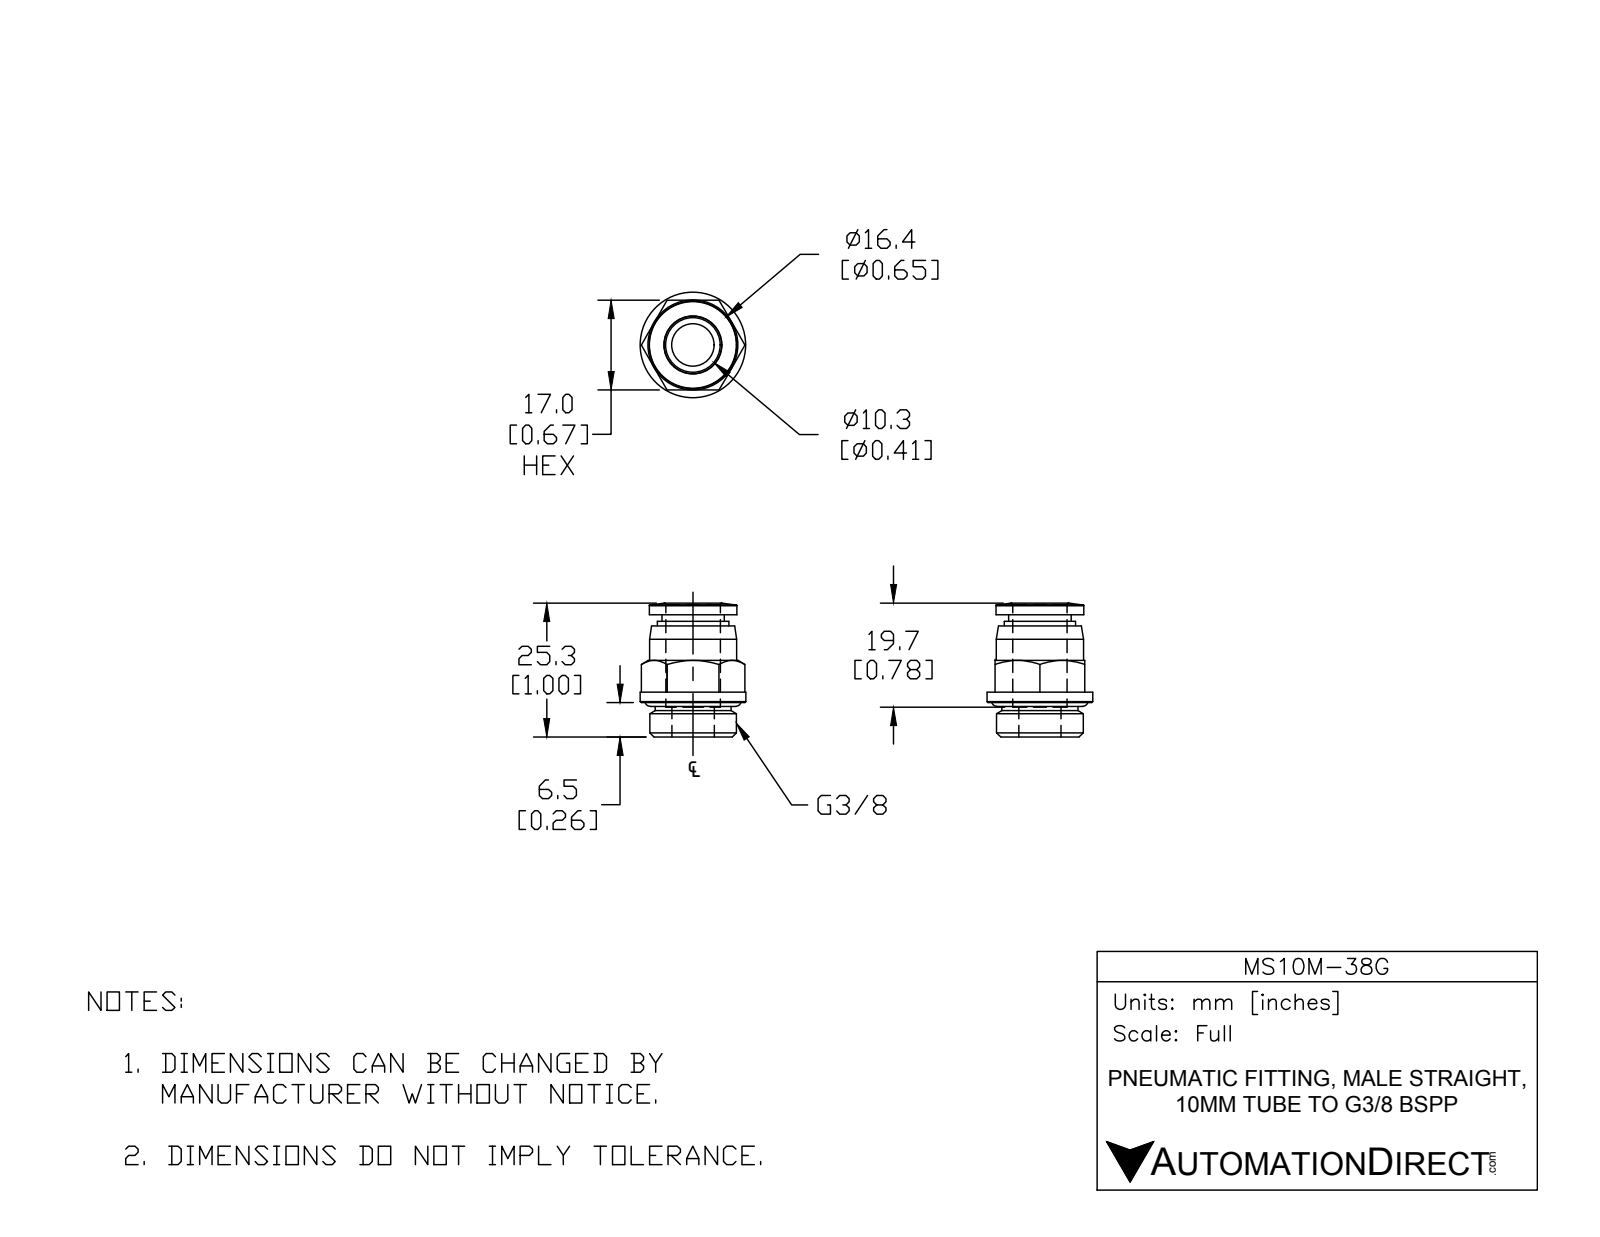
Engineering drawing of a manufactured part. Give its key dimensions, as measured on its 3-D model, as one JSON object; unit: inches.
{"part_name": "MS10M-38G", "step_written_by": "SolidWorks 2018 (AUTOMOTIVE_DESIGN)", "units": "inches", "bodies": {"solids": 2, "faces": 61, "planar": 16, "cylindrical": 18, "other": 27}, "overall_size": [0.998, 0.787, 0.787], "volume_in3": 0.22, "surface_area_in2": 4.992, "round_holes": [[0.315, 1], [0.406, 1]], "round_bosses_or_shafts": [[0.787, 1], [0.654, 1], [0.65, 1], [0.646, 1], [0.567, 1], [0.531, 1], [0.465, 1]], "face_to_face_distances": [0.669, 0.911, 0.335, 0.577, 0.827, 0.492, 0.085, 0.256, 0.571, 0.862]}
